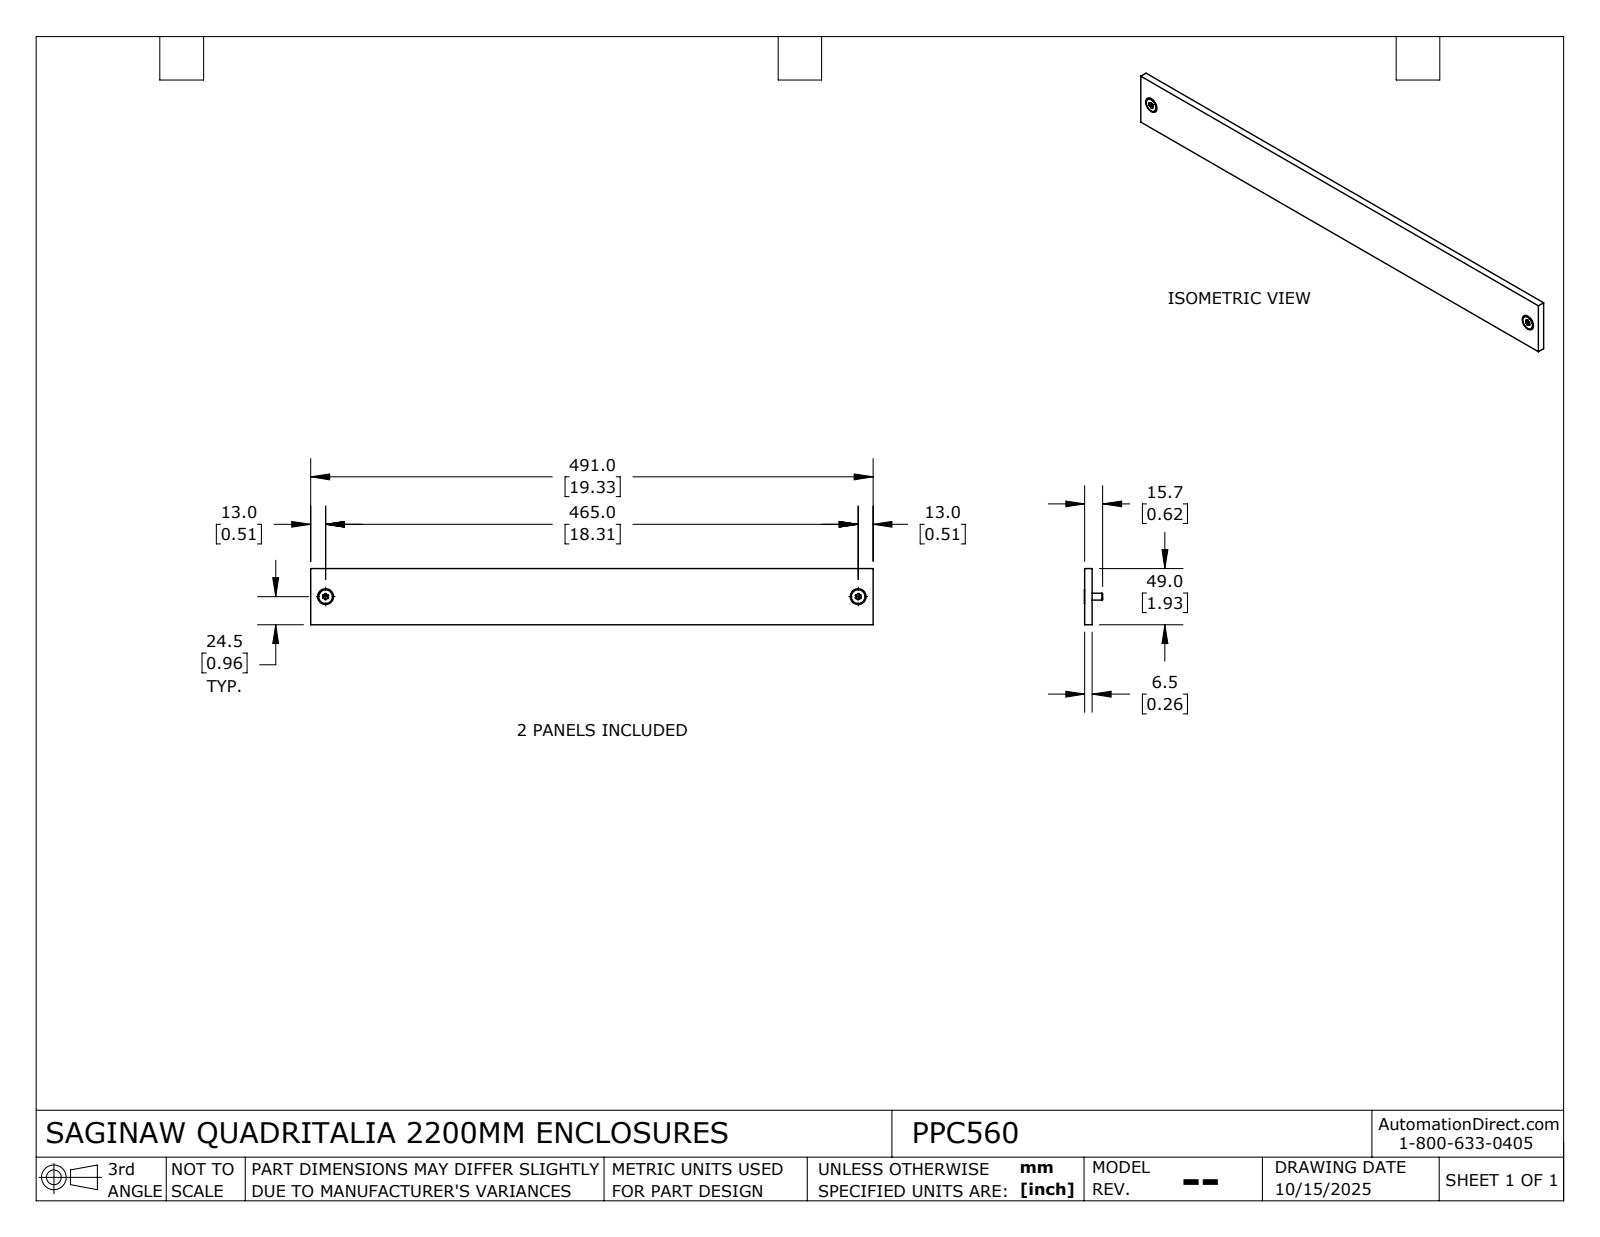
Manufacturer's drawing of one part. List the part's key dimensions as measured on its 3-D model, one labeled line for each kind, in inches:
Part name (STEP PRODUCT): PPC560
STEP written by: SolidWorks 2024 (AUTOMOTIVE_DESIGN)
Units: inches
Bodies: 2 solids, 182 faces (86 planar, 68 cylindrical, 28 other)
Overall size (bounding box): 74.764 × 19.331 × 0.63
Volume: 5.504 in³ · Surface area: 189.8 in²
Round holes (diameter × count): ⌀0.156 ×4
Round bosses / shafts (diameter × count): ⌀0.472 ×4, ⌀0.236 ×4
Partial cylindrical surfaces — rounded edges, fillets, slot ends (radius × count): R0.02 ×48
Main face-to-face distances: 0.059, 72.835, 1.87, 1.929, 74.705, 72.776, 72.894, 70.965, 1.811, 0.256
Hole centre spacings: 18.307, 72.835, 75.1
